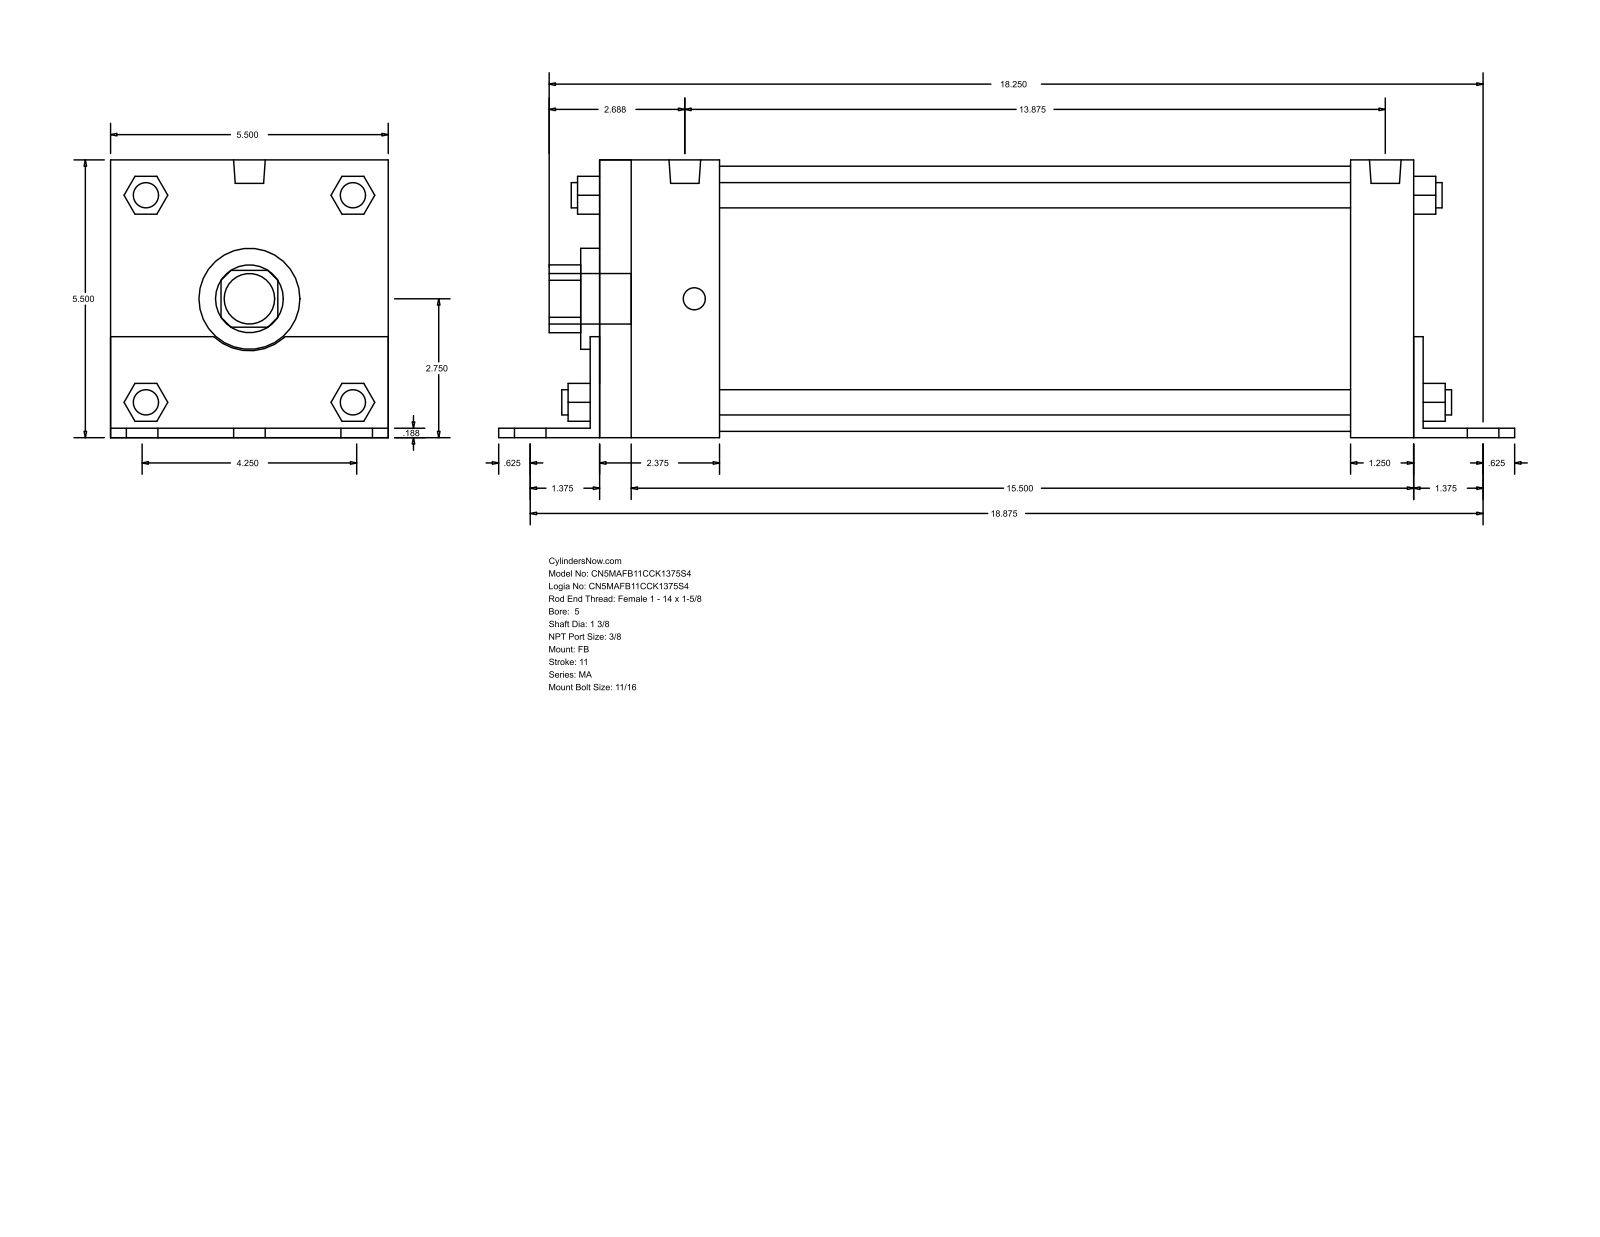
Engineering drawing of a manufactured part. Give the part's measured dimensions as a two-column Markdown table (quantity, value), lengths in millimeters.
| quantity | value |
| --- | --- |
| part name | MA_FB__0500_1.375 |
| STEP written by | GSSL Pune (CONFIG_CONTROL_DESIGN) |
| units | millimeters |
| bodies | 0 solids, 140 faces (105 planar, 35 cylindrical, 0 other) |
| overall size | 511.18 × 139.75 × 139.7 |
| round holes (diameter × count) | 34.92 × 1, 50.8 × 1, 133.35 × 1 |
| round bosses / shafts (diameter × count) | 17.46 × 6, 12.7 × 4, 11.11 × 4, 15.93 × 2, 25.4 × 1 |
| partial cylindrical surfaces (radius × count) | 17.06 × 1, 26.16 × 1 |
| main face-to-face distances | 139.7, 4.76, 139.75, 414.34, 4.71, 134.99, 409.58, 419.1, 31.75, 36.51 |
